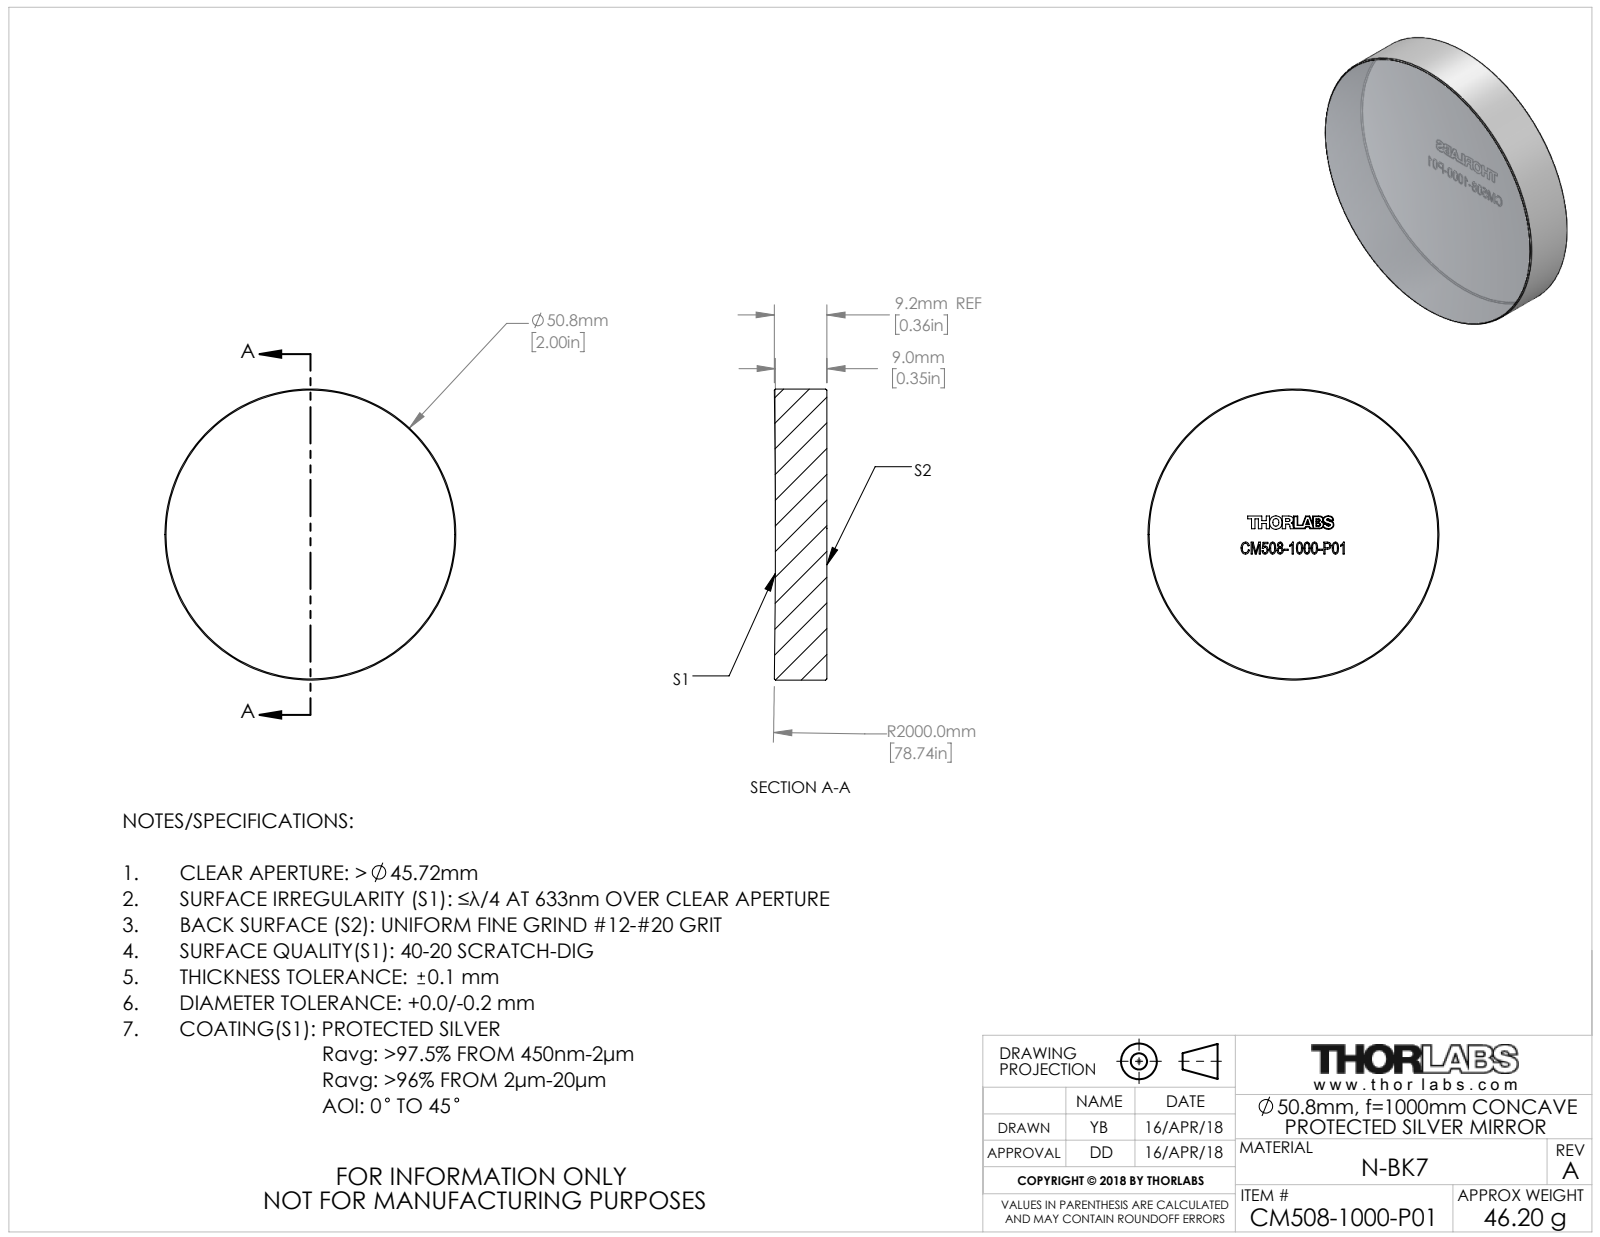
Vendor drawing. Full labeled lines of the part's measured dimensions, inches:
Part name (STEP PRODUCT): TTN153339-E0W
STEP written by: SolidWorks 2018 (CONFIG_CONTROL_DESIGN)
Units: inches
Bodies: 1 solid, 46 faces (38 planar, 2 cylindrical, 6 other)
Overall size (bounding box): 2 × 2 × 0.361
Volume: 1.123 in³ · Surface area: 8.491 in²
Round bosses / shafts (diameter × count): ⌀2 ×1
